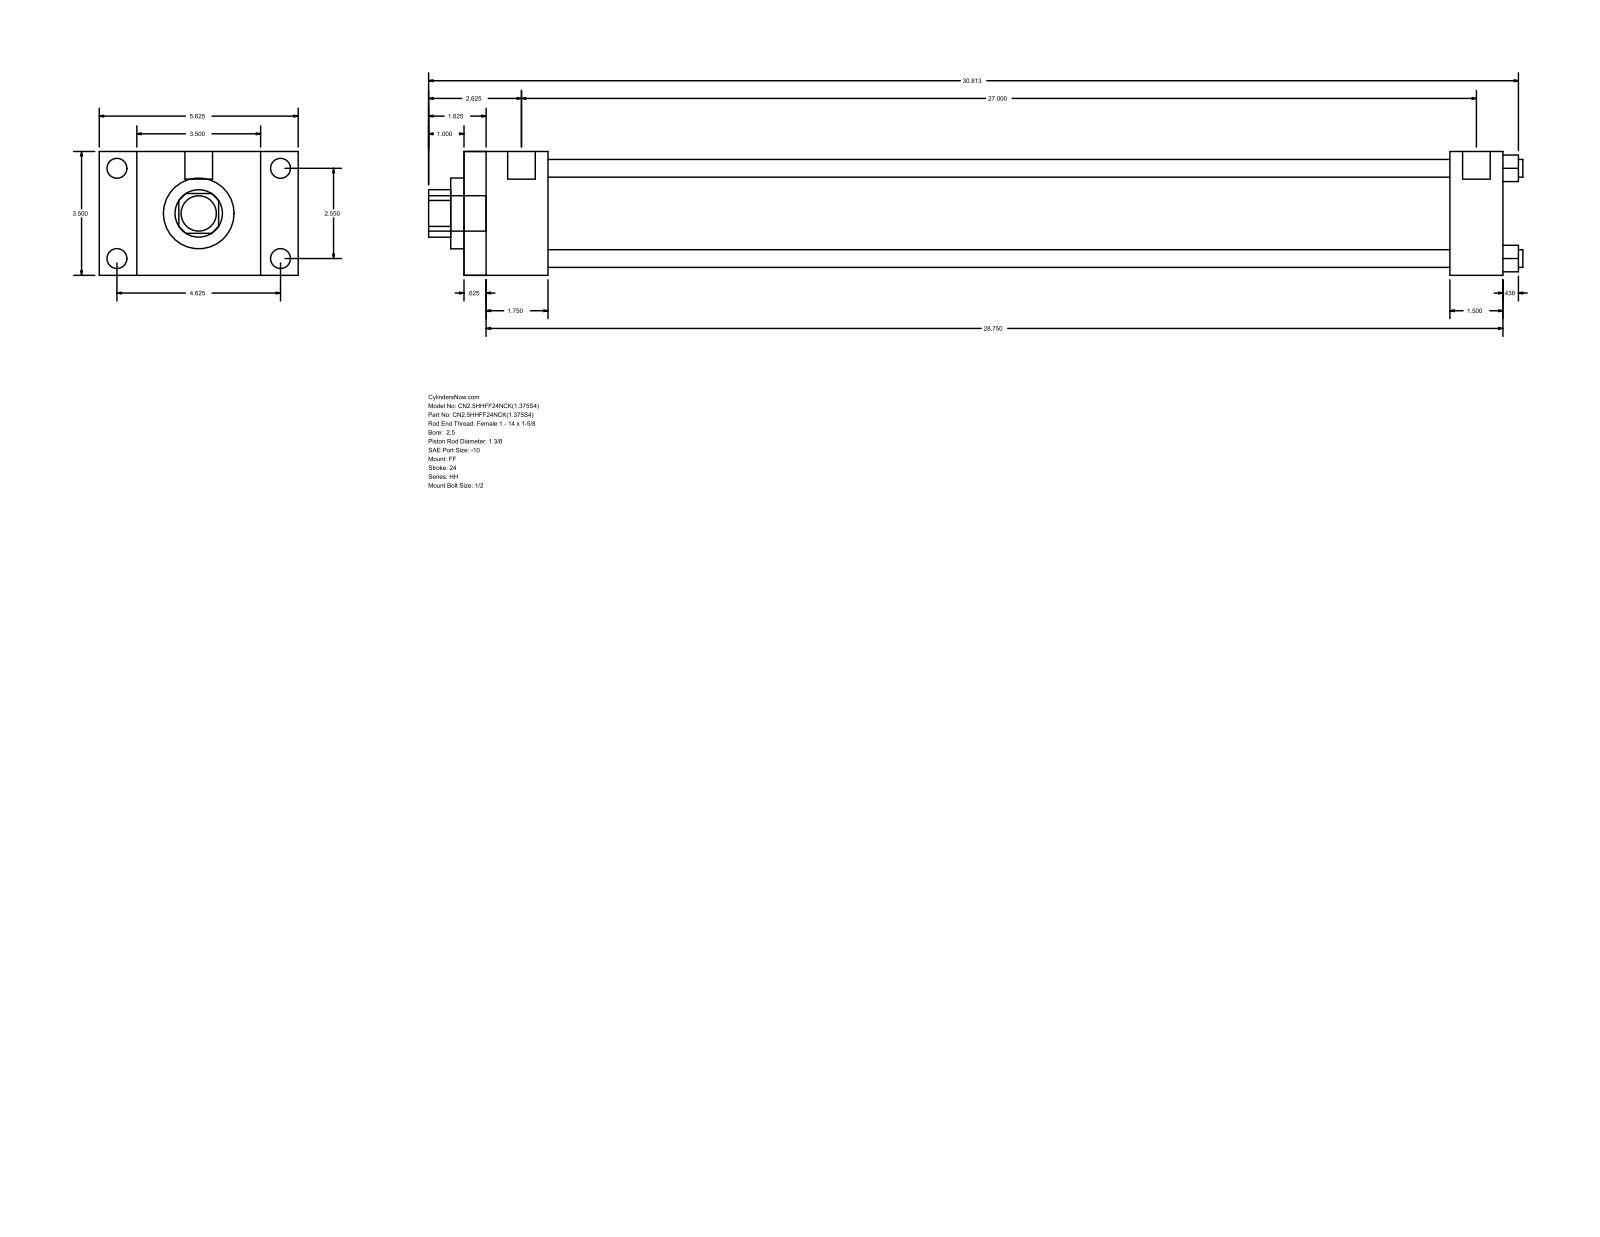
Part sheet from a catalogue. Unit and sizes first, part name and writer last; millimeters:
Units: millimetres
Overall size (bounding box): 785.81 × 142.88 × 88.9
Round holes (diameter × count): ⌀12.7 ×4, ⌀34.92 ×1, ⌀50.8 ×1, ⌀73.03 ×1
Round bosses / shafts (diameter × count): ⌀14.3 ×4, ⌀5.56 ×4, ⌀19.84 ×2, ⌀25.4 ×1
Partial cylindrical surfaces — rounded edges, fillets, slot ends (radius × count): R17.06 ×1
Main face-to-face distances: 88.9, 746.12, 15.87, 730.25, 60.32, 44.45, 685.8, 708.02, 692.15, 647.7
Hole centre spacings: 45.79, 64.76, 91.58
Bodies: 0 solids, 92 faces (64 planar, 28 cylindrical, 0 other)
Part name (STEP PRODUCT): HH_FF__0250_1.375
STEP written by: GSSL Pune (CONFIG_CONTROL_DESIGN)
